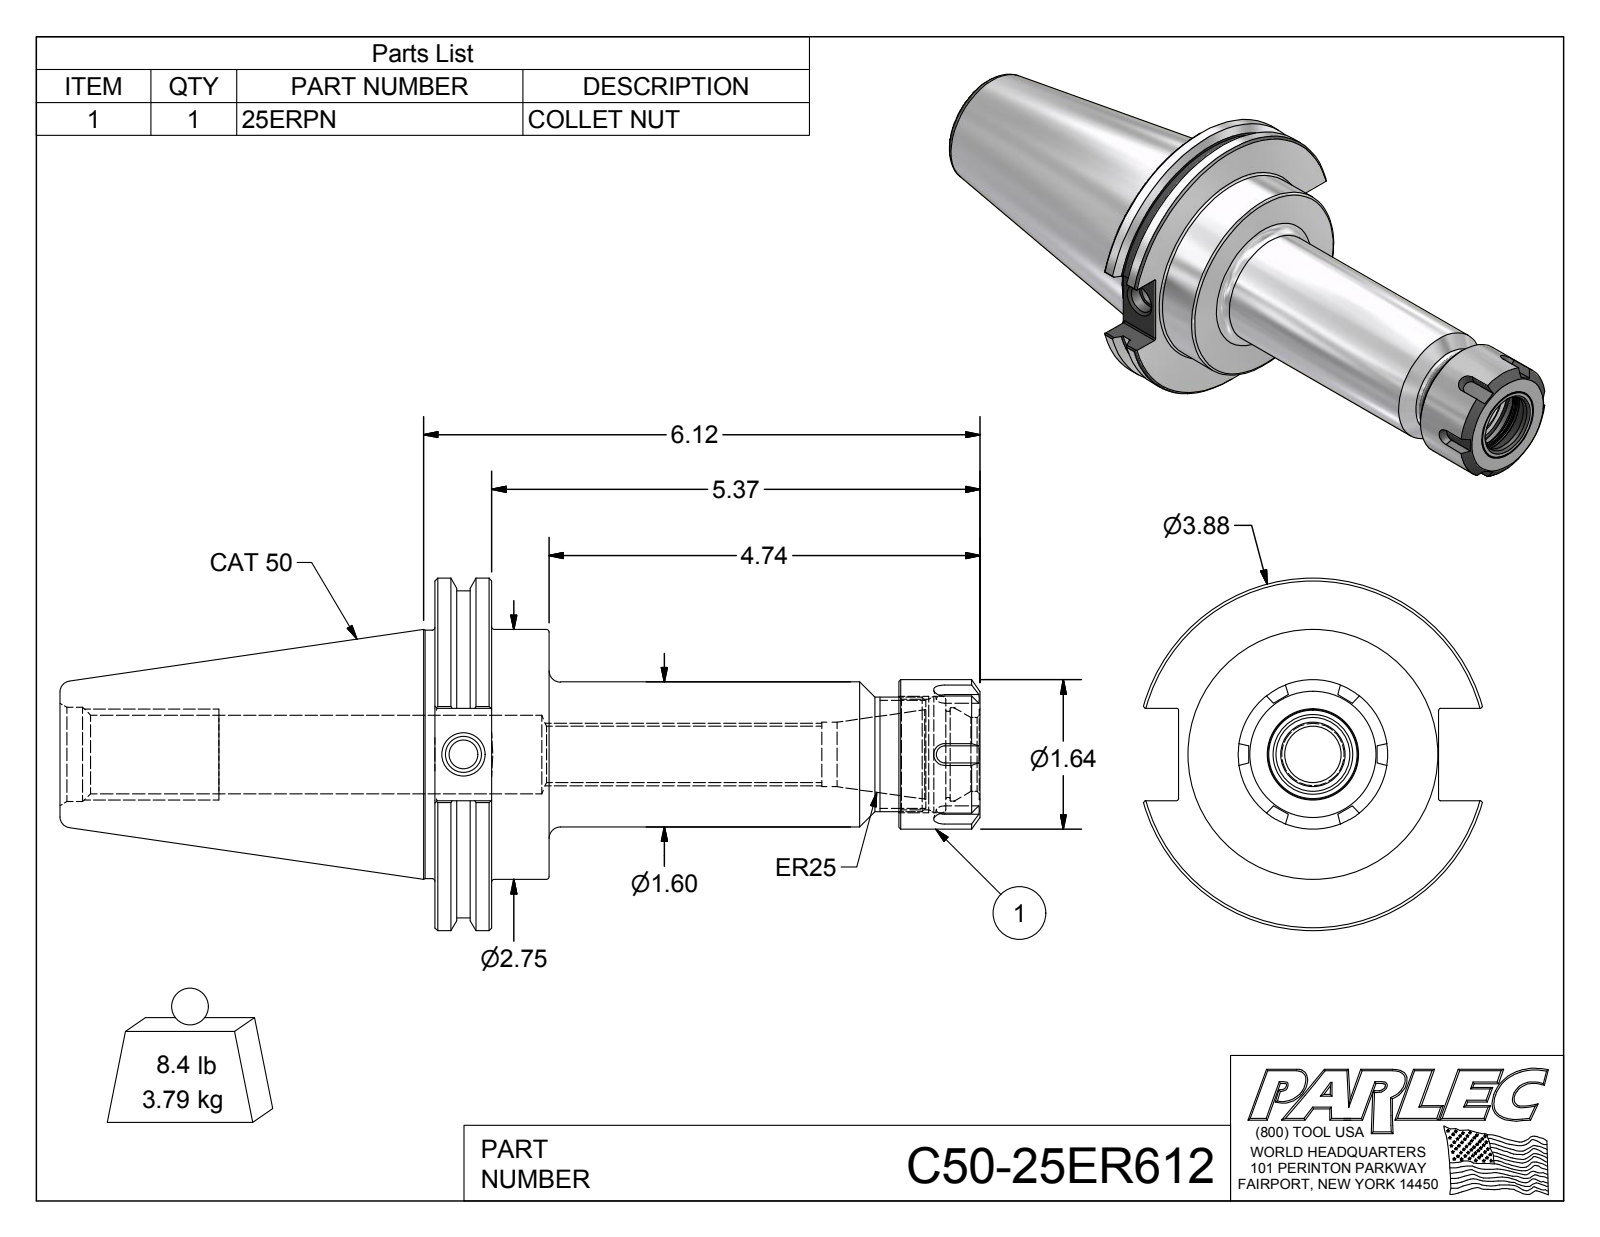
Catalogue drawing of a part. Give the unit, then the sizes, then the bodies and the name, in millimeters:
Units: millimetres
Overall size (bounding box): 257 × 98.4 × 94.7
Round holes (diameter × count): ⌀8 ×1, ⌀10.1 ×1, ⌀15.7 ×1, ⌀18 ×1, ⌀20.6 ×1, ⌀21.9 ×1, ⌀22 ×1, ⌀24.1 ×1, ⌀26.1 ×1, ⌀26.4 ×1, ⌀30.9 ×1, ⌀32.5 ×1
Round bosses / shafts (diameter × count): ⌀98.4 ×1, ⌀91.3 ×1, ⌀69.9 ×1, ⌀69.3 ×1, ⌀41.7 ×1, ⌀40.5 ×1, ⌀32 ×1
Partial cylindrical surfaces — rounded edges, fillets, slot ends (radius × count): R0.5 ×8
Main face-to-face distances: 15.9, 31.9, 16, 152.3, 136.4, 120.4, 129.6, 113.7, 97.7, 22.7
Volume: 491 300 mm³ · Surface area: 73 610 mm²
Bodies: 2 solids, 127 faces (52 planar, 31 cylindrical, 44 other)
Part name (STEP PRODUCT): C50-25ER612; C50-25ER6-1; 25ERPN
STEP written by: Autodesk Inventor 2012 (AUTOMOTIVE_DESIGN)
